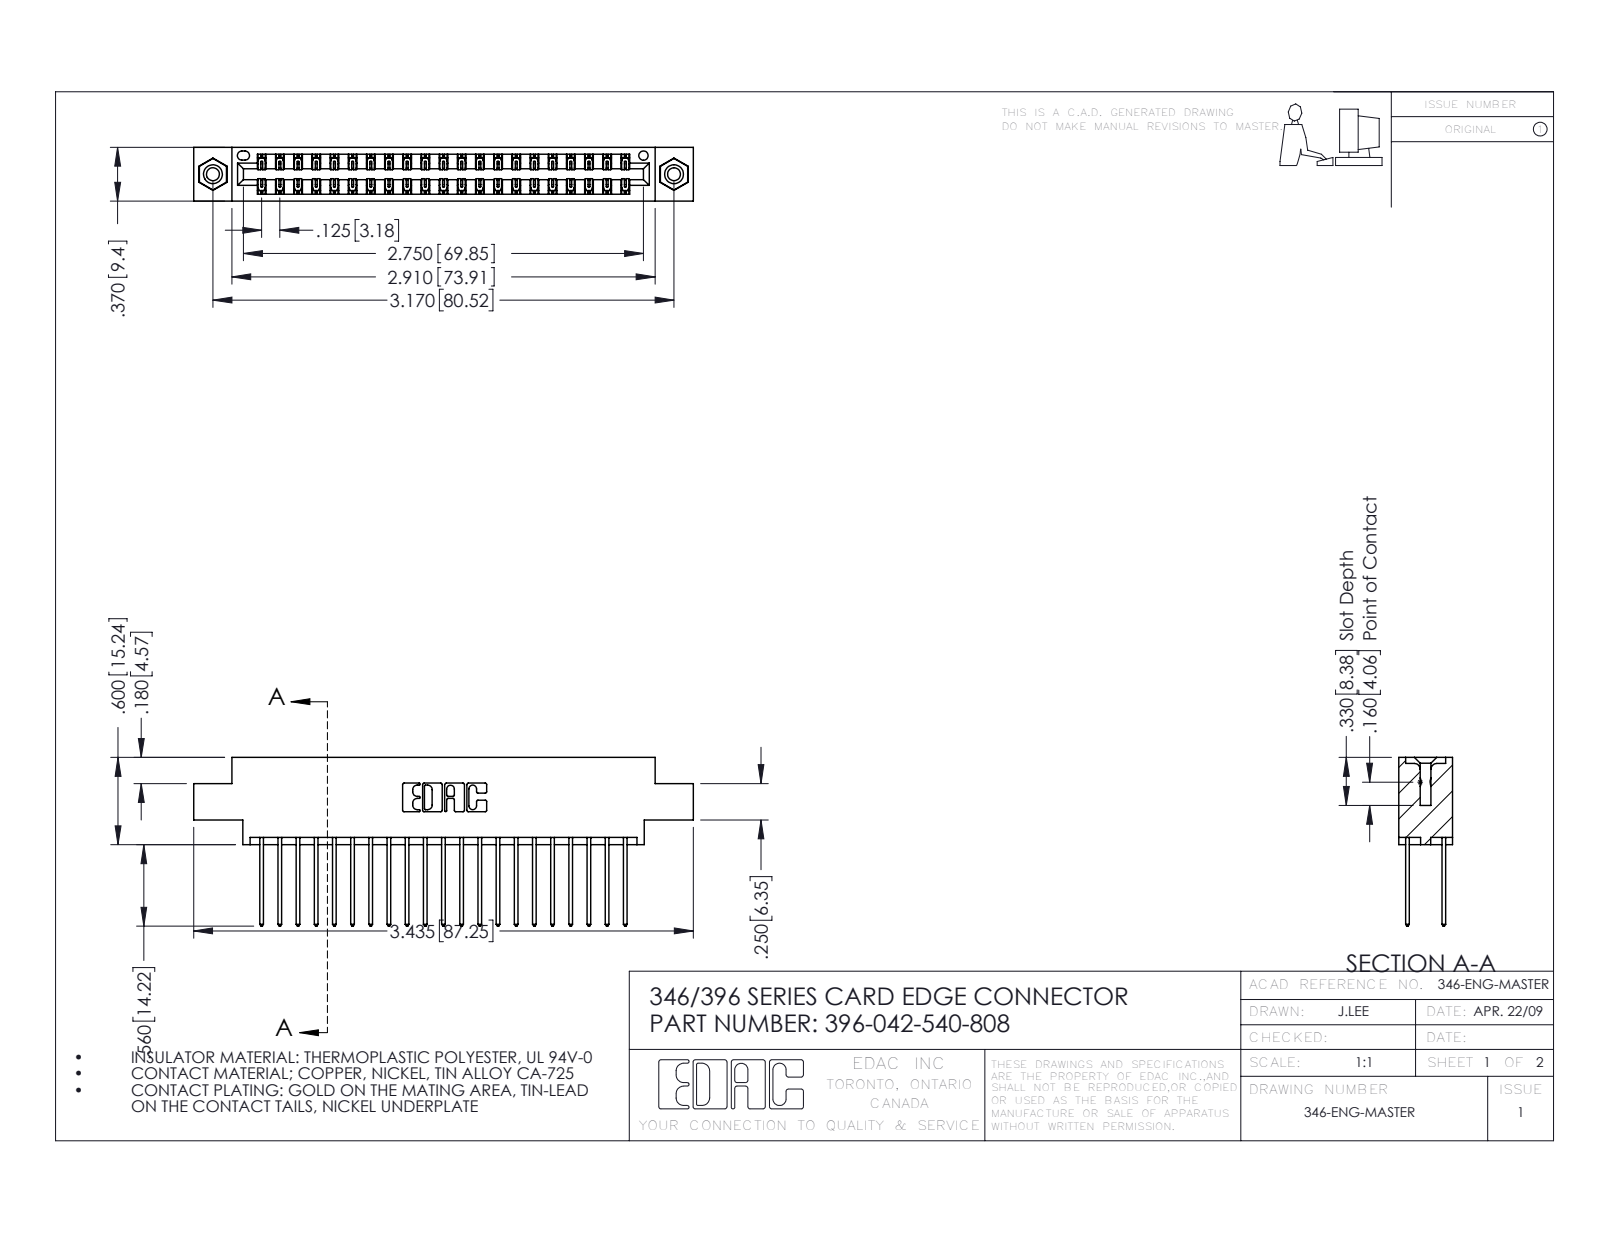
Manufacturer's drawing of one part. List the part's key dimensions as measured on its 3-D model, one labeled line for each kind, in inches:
Part name (STEP PRODUCT): 396-042-540-808; 346 Part_0.170 Offset - 0.156 Dia-TI; 345-250-001_345-250-003-102; 345-292-001_345-293-140
STEP written by: SolidWorks 2016 (CONFIG_CONTROL_DESIGN)
Units: inches
Bodies: 45 solids, 2370 faces (1582 planar, 772 cylindrical, 16 other)
Overall size (bounding box): 3.435 × 1.16 × 0.37
Volume: 0.509 in³ · Surface area: 18.74 in²
Round holes (diameter × count): ⌀0.089 ×2, ⌀0.125 ×2, ⌀0.156 ×2, ⌀0.064 ×1
Round bosses / shafts (diameter × count): ⌀0.155 ×2
Partial cylindrical surfaces — rounded edges, fillets, slot ends (radius × count): R0.006 ×63, R0.01 ×42, R0.01 ×22, R0.007 ×6, R0.031 ×6, R0.026 ×3, R0.014 ×2, R0.022 ×2
Main face-to-face distances: 0.048, 0.322, 0.25, 0.37, 0.072, 0.298, 0.025, 0.275, 0.222, 0.148
Hole centre spacings: 0.246, 2.963, 3.17
